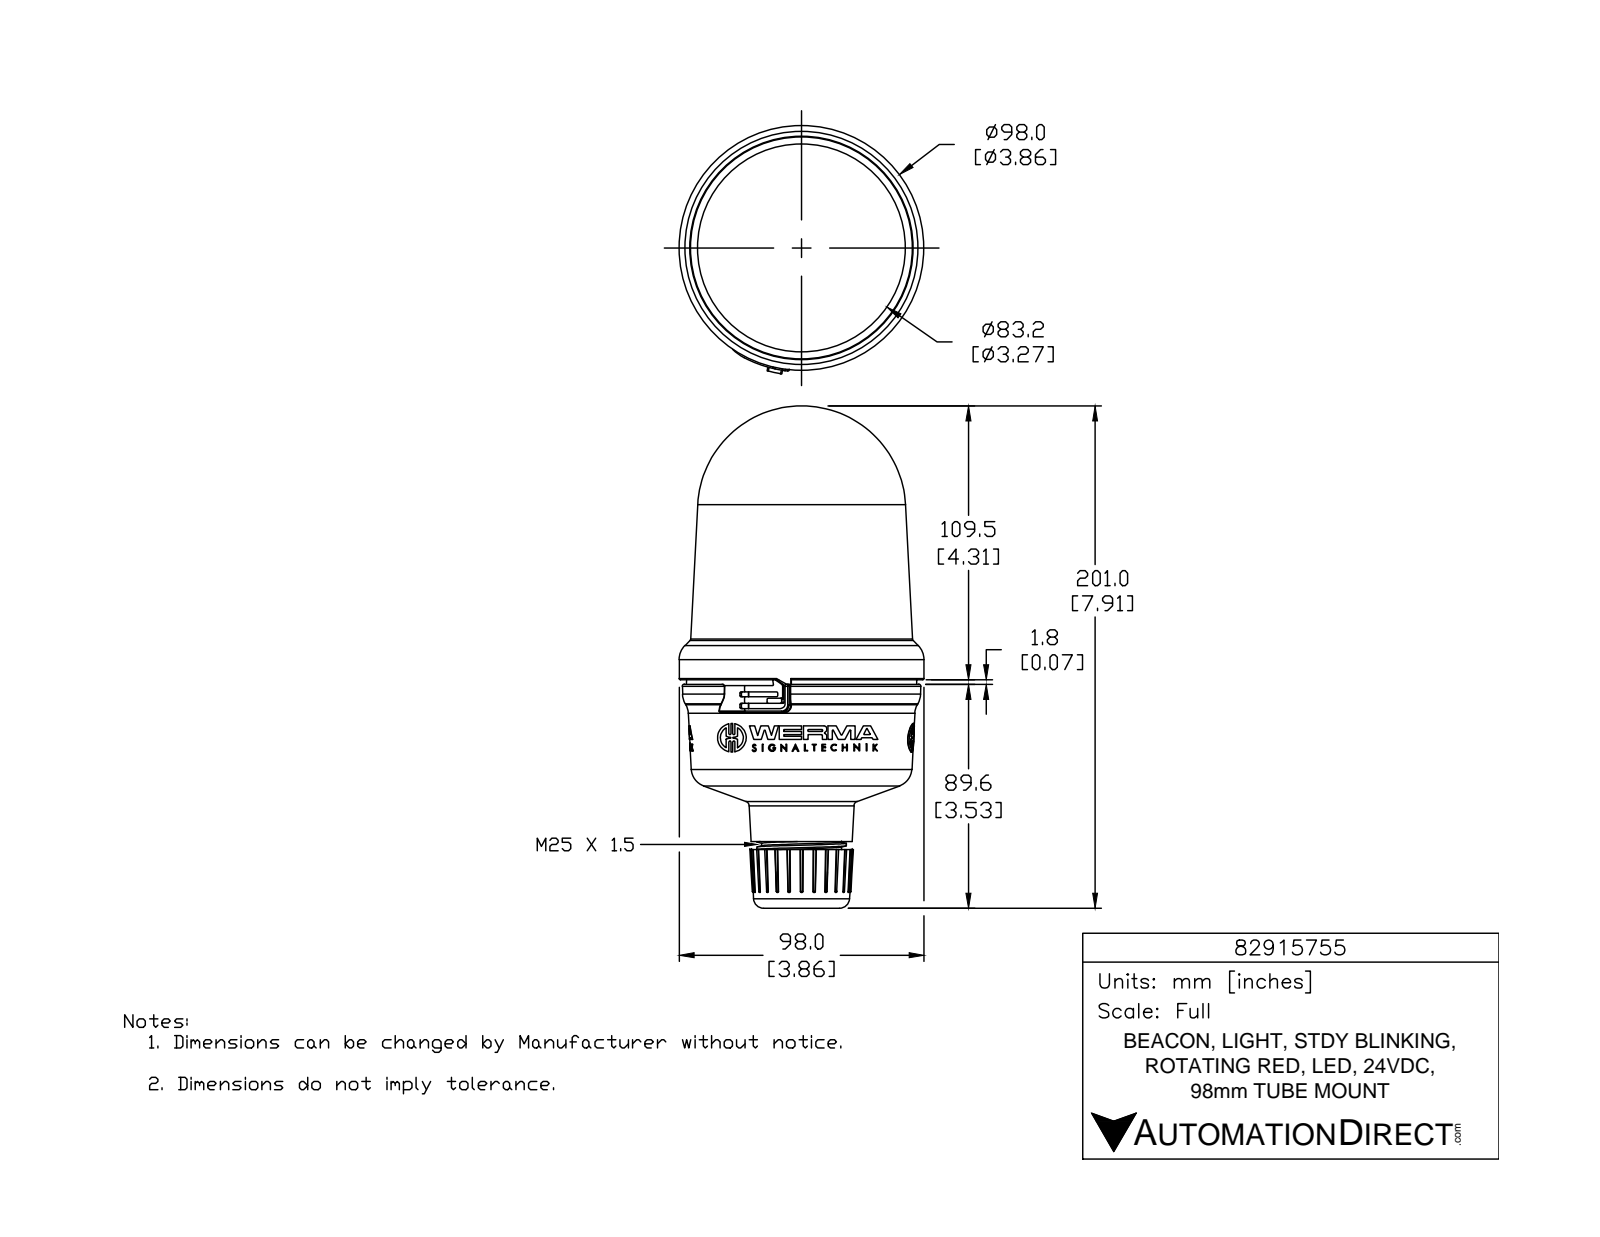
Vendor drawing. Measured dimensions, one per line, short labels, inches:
name: 82915755
written by: SolidWorks 2015 (AUTOMOTIVE_DESIGN)
unit: in
bodies: 1 solid, 1006 faces (554 planar, 189 cylindrical, 263 other)
size: 7.914 × 3.912 × 3.858
volume: 54.7 in³; area: 91.39 in²
holes: 3× ⌀0.078, 1× ⌀1.013, 1× ⌀1.024
bosses: 3× ⌀0.452, 3× ⌀0.113, 1× ⌀3.858, 1× ⌀1.409, 1× ⌀1.261
rounds: 12× R0.02, 9× R0.007, 6× R0.007, 6× R0.016, 6× R0.016, 6× R0.016, 6× R0.262, 3× R0.006
face distances: 2.214, 0.462, 2.676, 0.335, 0.127, 2.548, 2.603, 2.476, 2.141, 0.073
